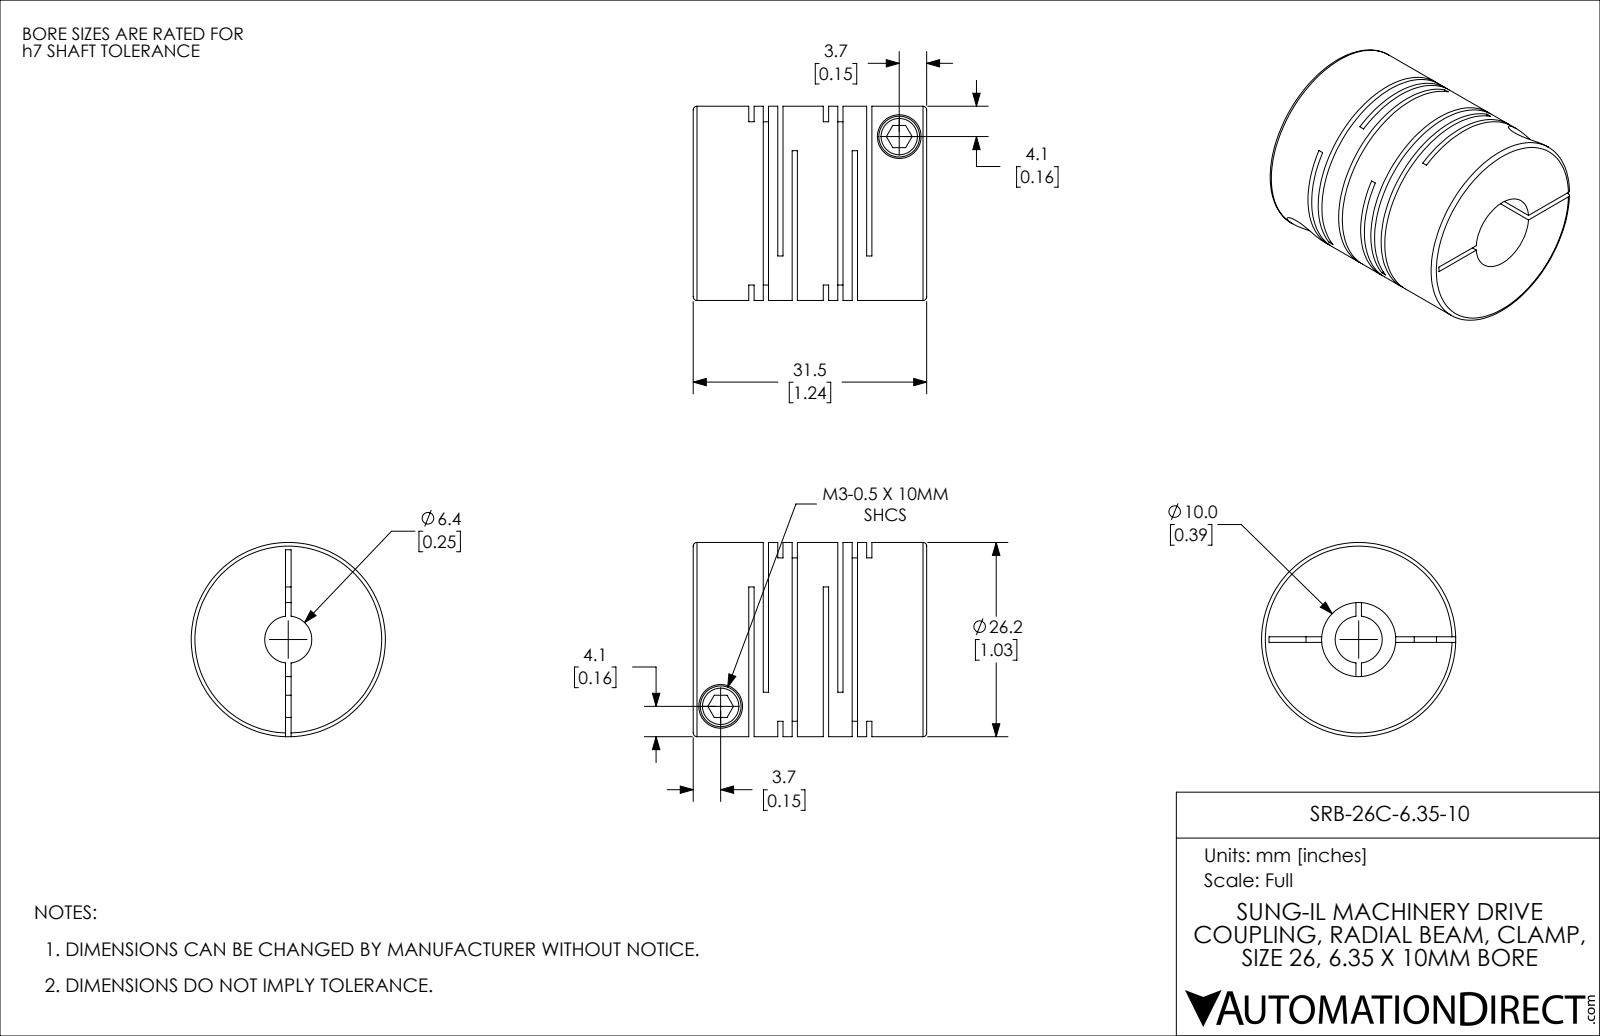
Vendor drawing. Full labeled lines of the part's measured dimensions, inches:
Part name (STEP PRODUCT): SRB-26C-6.35-10
STEP written by: SolidWorks 2021 (CONFIG_CONTROL_DESIGN)
Units: inches
Bodies: 1 solid, 114 faces (60 planar, 42 cylindrical, 12 other)
Overall size (bounding box): 1.24 × 1.031 × 1.031
Volume: 0.749 in³ · Surface area: 16.71 in²
Round holes (diameter × count): ⌀0.118 ×2, ⌀0.232 ×2, ⌀0.25 ×1, ⌀0.394 ×1
Round bosses / shafts (diameter × count): ⌀0.217 ×2, ⌀1.031 ×1
Main face-to-face distances: 0.077, 0.396, 0.028, 0.154, 0.319, 0.472, 0.049, 0.105, 0.368, 0.549
